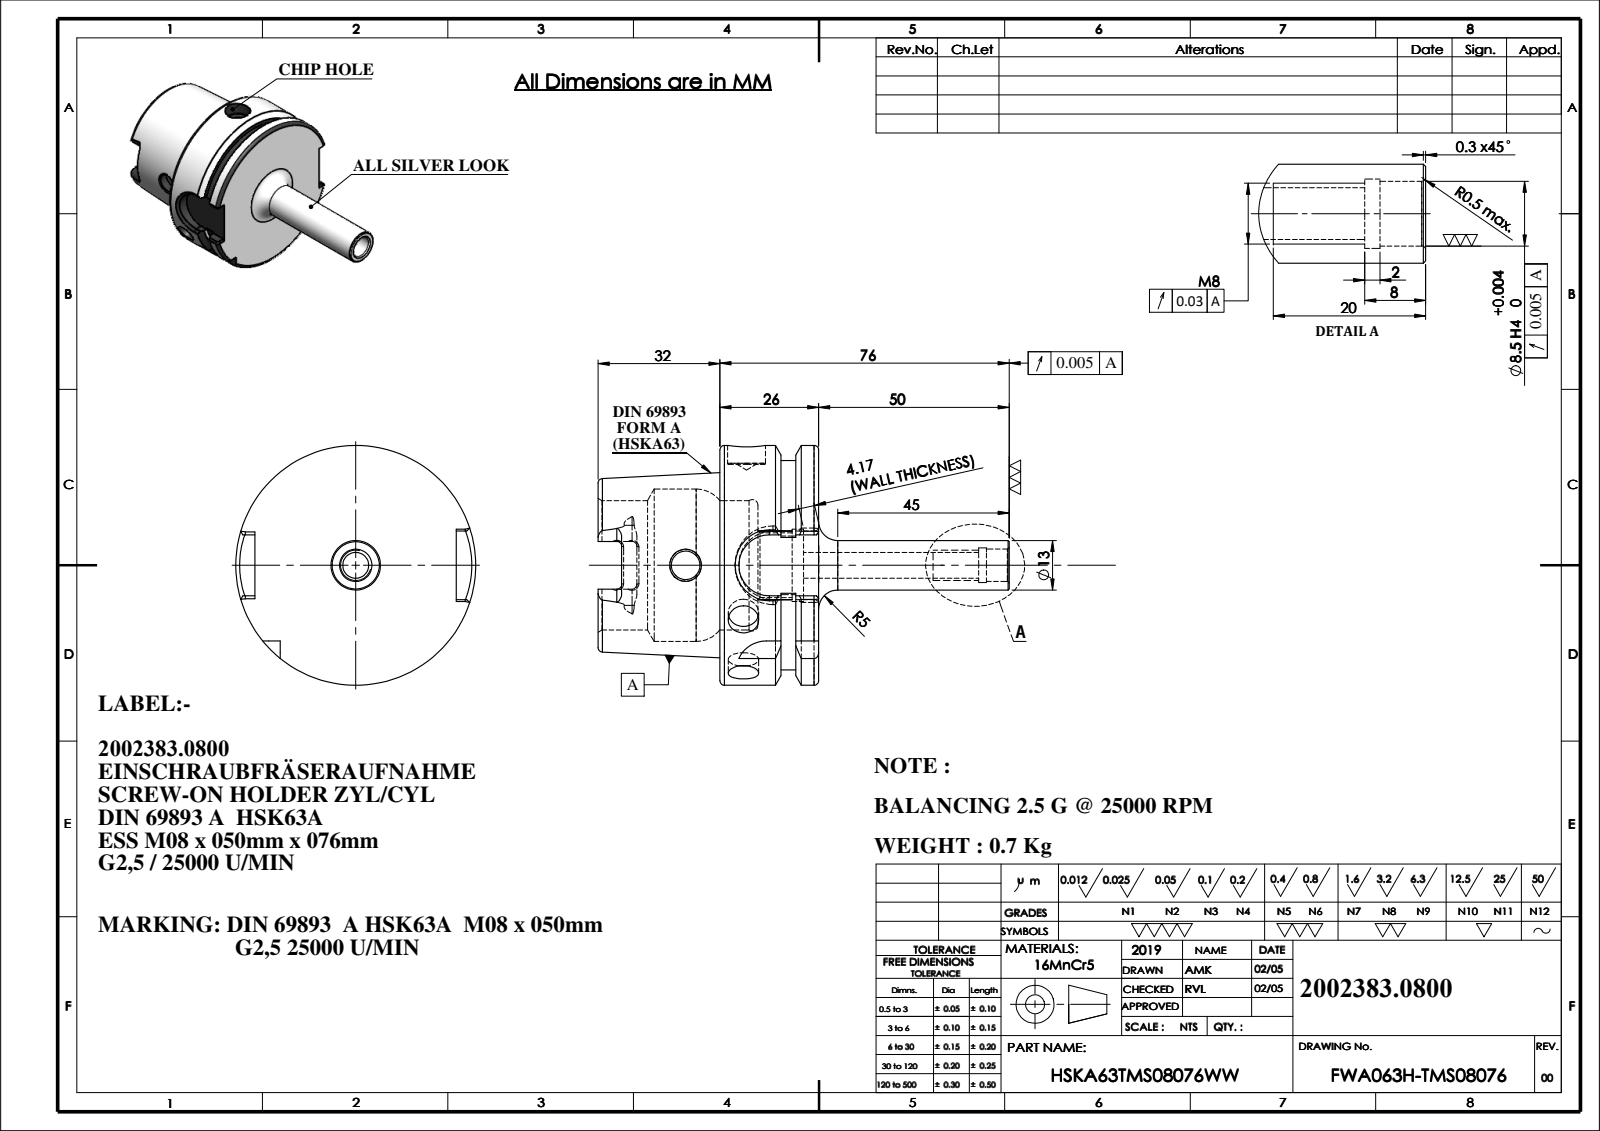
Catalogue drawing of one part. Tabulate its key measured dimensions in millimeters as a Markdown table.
| quantity | value |
| --- | --- |
| part name | FWA063H-TMS08076; HSKA63TMS08076WW |
| STEP written by | SolidWorks 2023 (CONFIG_CONTROL_DESIGN) |
| units | millimeters |
| bodies | 1 solid, 164 faces (51 planar, 51 cylindrical, 62 other) |
| overall size | 108 × 63 × 63 |
| volume | 85 785 mm³ |
| surface area | 25 444 mm² |
| round holes (diameter × count) | 8 × 2, 6.8 × 1, 7.5 × 1, 8.5 × 1, 9.1 × 1, 10 × 1, 17 × 1, 19 × 1, 34 × 1, 40 × 1 |
| round bosses / shafts (diameter × count) | 63 × 1, 55 × 1, 13 × 1 |
| partial cylindrical surfaces (radius × count) | 1.3 × 6, 2.88 × 4, 8 × 2, 9 × 1 |
| main face-to-face distances | 25.95, 10, 15.95, 32, 42, 57.95, 52.9, 54, 22, 12 |
